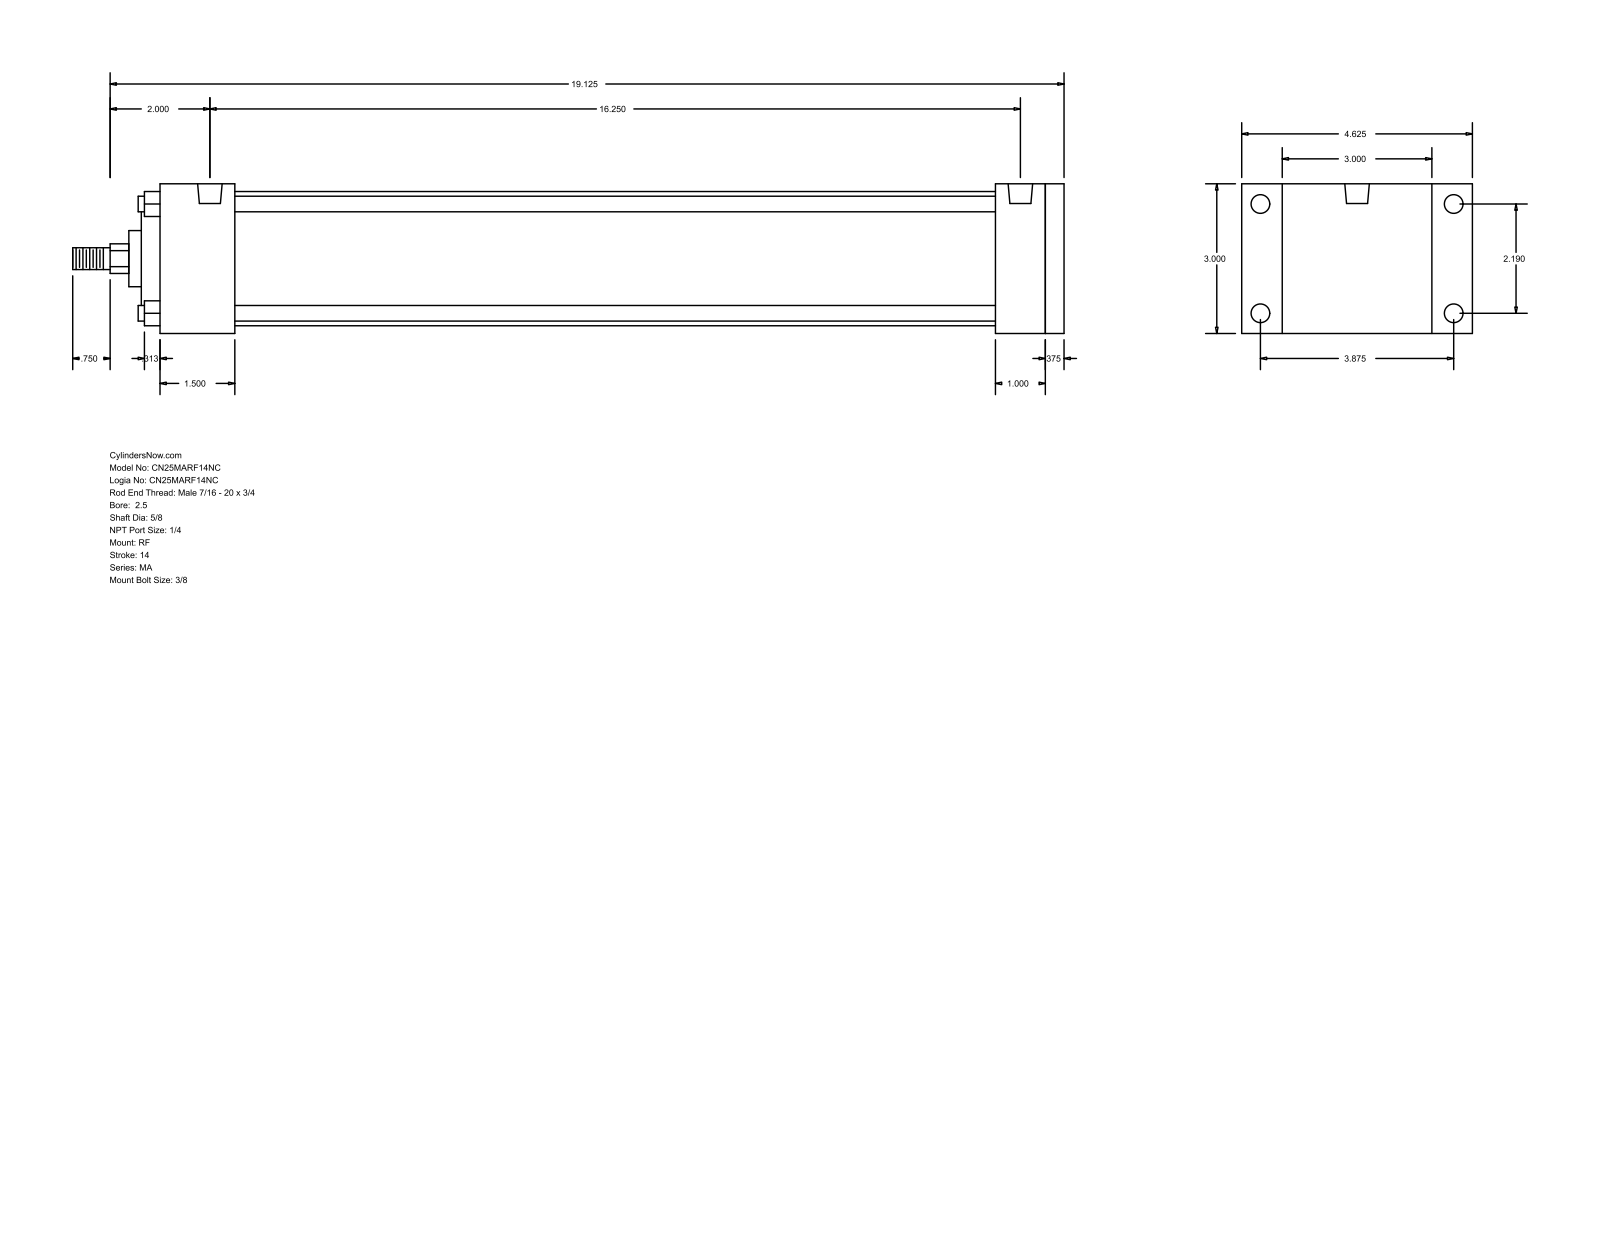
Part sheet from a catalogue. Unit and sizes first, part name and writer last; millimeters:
Units: millimetres
Overall size (bounding box): 504.82 × 117.47 × 76.2
Round holes (diameter × count): ⌀7.94 ×4, ⌀9.53 ×4, ⌀12.49 ×2
Round bosses / shafts (diameter × count): ⌀7.94 ×4, ⌀68.33 ×1, ⌀50.8 ×1, ⌀28.57 ×1, ⌀15.88 ×1, ⌀11.11 ×1
Partial cylindrical surfaces — rounded edges, fillets, slot ends (radius × count): R7.54 ×1
Main face-to-face distances: 76.2, 460.37, 9.52, 450.85, 25.4, 38.1, 425.45, 387.35, 412.75, 422.27
Hole centre spacings: 55.62, 98.42, 113.05, 412.75
Bodies: 0 solids, 94 faces (65 planar, 29 cylindrical, 0 other)
Part name (STEP PRODUCT): MA_RF__0250_0.625
STEP written by: GSSL Pune (CONFIG_CONTROL_DESIGN)
